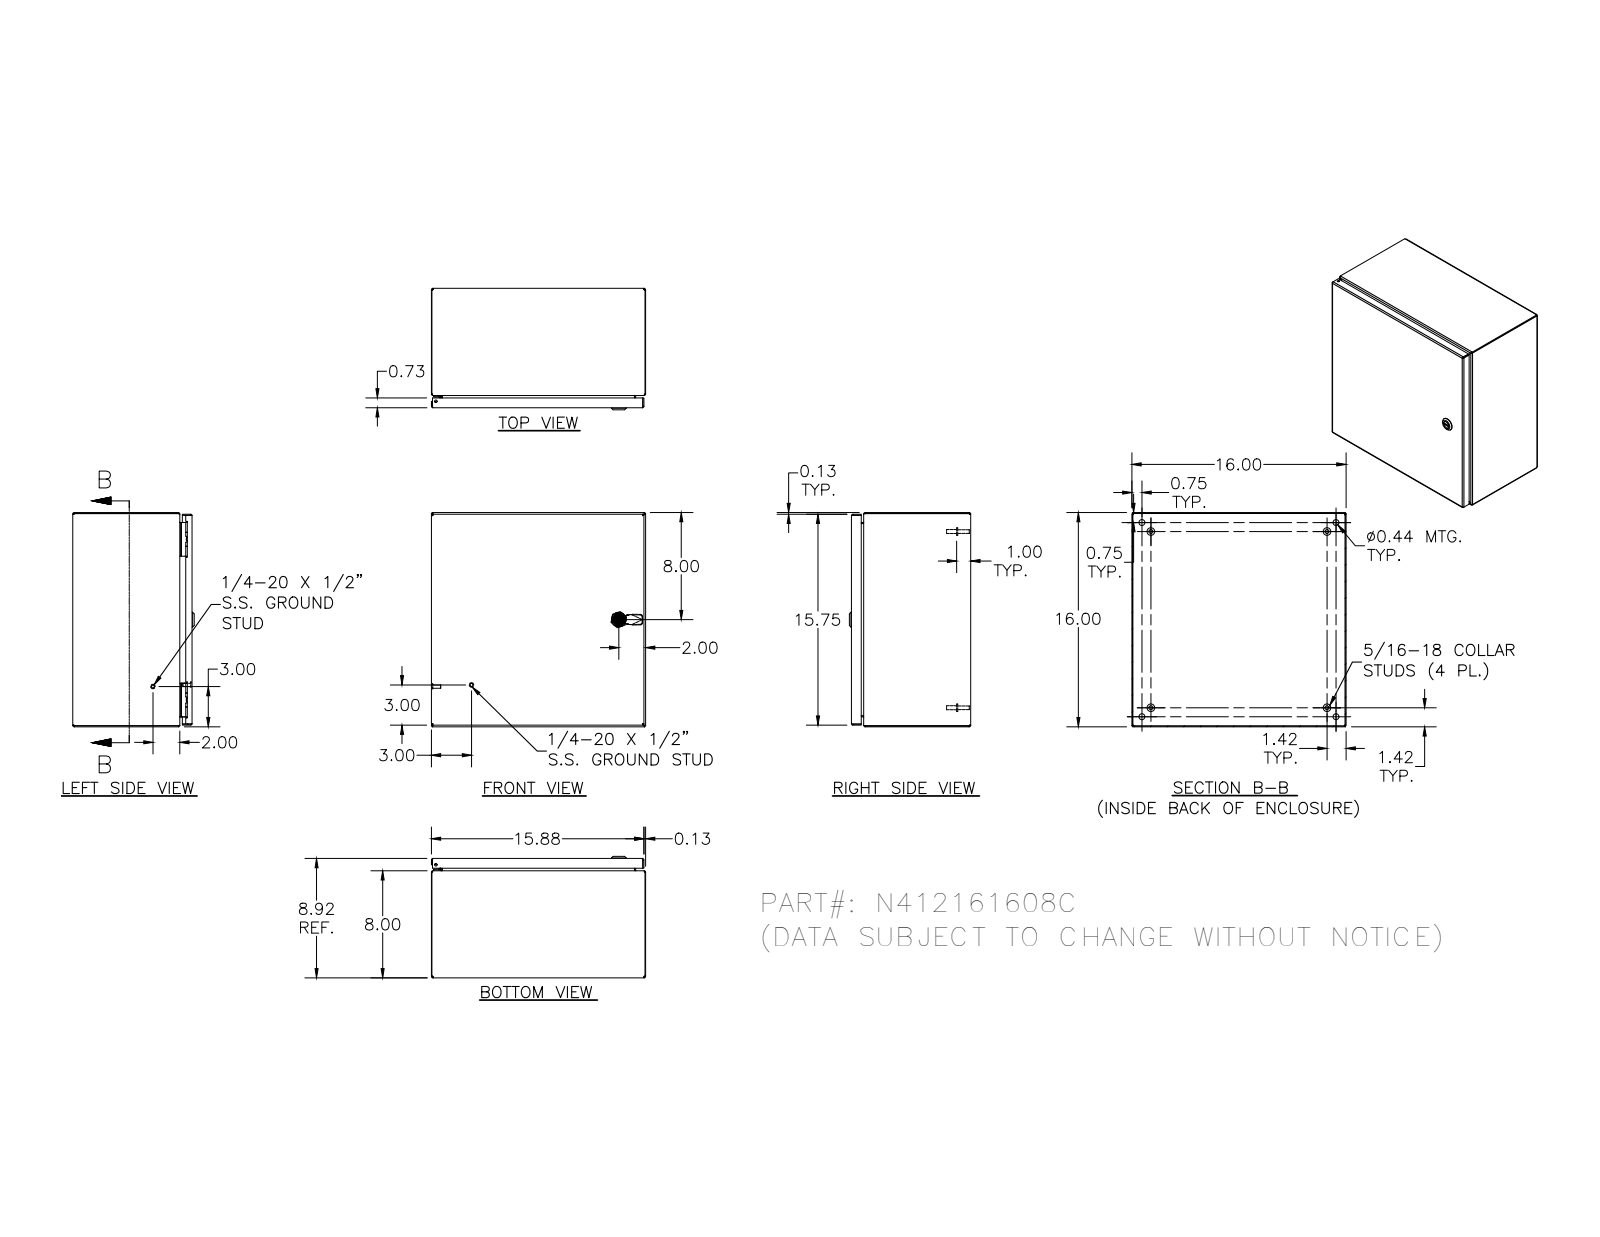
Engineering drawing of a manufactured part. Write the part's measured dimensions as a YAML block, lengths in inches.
part_name: "N412161608C"
step_written_by: "SolidWorks 2018 (AUTOMOTIVE_DESIGN)"
units: inches
bodies: {solids: 33, faces: 1449, planar: 530, cylindrical: 547, other: 372}
overall_size: [16, 16, 9.075]
volume: 85.74
surface_area: 2334
round_holes:
  - {diameter: 0.188, count: 5}
  - {diameter: 0.093, count: 4}
  - {diameter: 0.152, count: 4}
  - {diameter: 0.167, count: 4}
  - {diameter: 0.172, count: 4}
  - {diameter: 0.437, count: 4}
  - {diameter: 0.156, count: 2}
  - {diameter: 0.187, count: 1}
  - {diameter: 0.197, count: 1}
  - {diameter: 0.315, count: 1}
  - {diameter: 0.394, count: 1}
  - {diameter: 0.402, count: 1}
round_bosses_or_shafts:
  - {diameter: 0.25, count: 10}
  - {diameter: 0.131, count: 5}
  - {diameter: 0.563, count: 4}
  - {diameter: 0.36, count: 4}
  - {diameter: 0.32, count: 4}
  - {diameter: 0.3, count: 4}
  - {diameter: 0.275, count: 4}
  - {diameter: 0.256, count: 4}
partial_cylinders:
  - {radius: 0.012, count: 30}
  - {radius: 0.031, count: 30}
  - {radius: 0.05, count: 26}
  - {radius: 0.105, count: 20}
  - {radius: 0.016, count: 18}
  - {radius: 0.125, count: 16}
  - {radius: 0.02, count: 13}
  - {radius: 0.032, count: 8}
face_to_face_distances: [0.074, 8.843, 15.926, 15.852, 0.074, 15.926, 16, 8.769, 8.917, 0.917]
hole_center_spacings: [12, 0.66, 0.656, 1.307, 1.965, 11.34, 12.66, 14.5]
